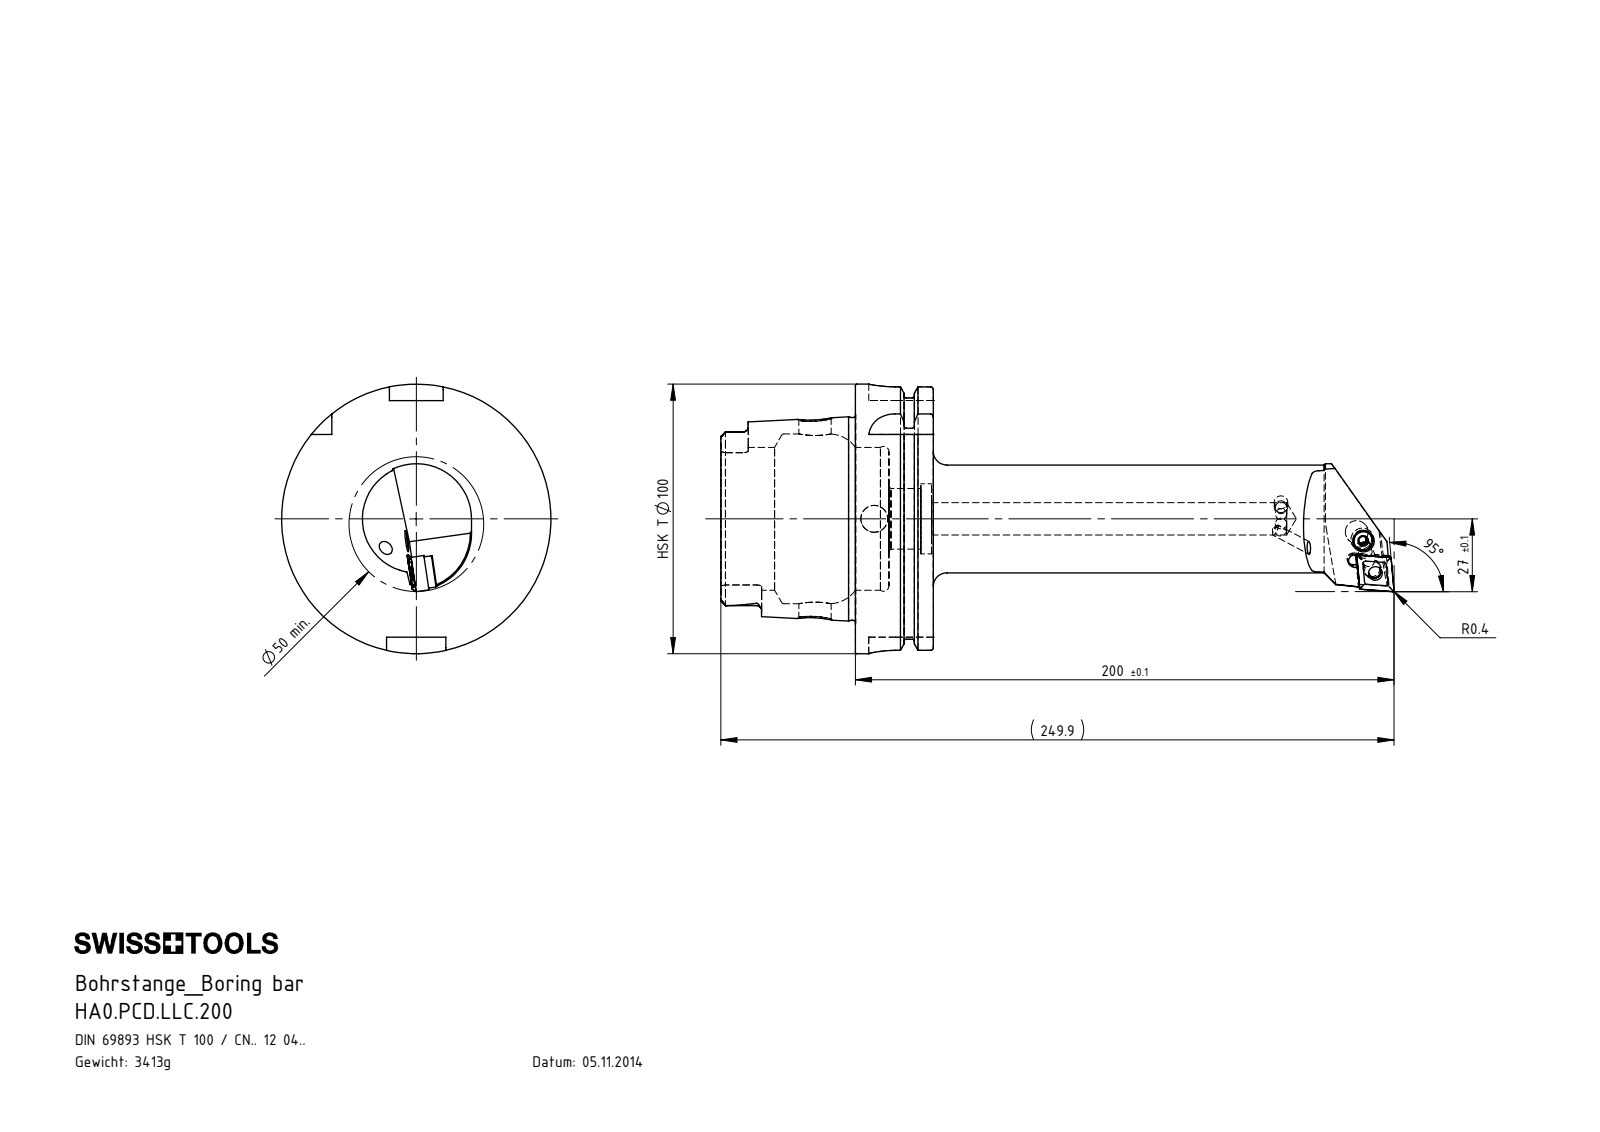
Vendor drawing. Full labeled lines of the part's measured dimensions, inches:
Part name (STEP PRODUCT): WCD-ER3.101.000_A; WCD-ER4.101.017_A; KVT_MB_600_050; CNMG120404 (+3 more)
STEP written by: SolidWorks 2017 (AUTOMOTIVE_DESIGN)
Units: inches
Bodies: 7 solids, 281 faces (112 planar, 69 cylindrical, 100 other)
Overall size (bounding box): 9.839 × 3.937 × 3.937
Volume: 26.47 in³ · Surface area: 120.8 in²
Round holes (diameter × count): ⌀0.165 ×2, ⌀0.472 ×2, ⌀0.157 ×1, ⌀0.203 ×1, ⌀0.252 ×1, ⌀0.276 ×1, ⌀0.331 ×1, ⌀0.394 ×1, ⌀0.886 ×1, ⌀1.024 ×1, ⌀2.087 ×1, ⌀2.48 ×1
Round bosses / shafts (diameter × count): ⌀3.937 ×1, ⌀3.62 ×1, ⌀2.963 ×1, ⌀1.575 ×1, ⌀0.315 ×1, ⌀0.311 ×1, ⌀0.252 ×1, ⌀0.197 ×1
Partial cylindrical surfaces — rounded edges, fillets, slot ends (radius × count): R0.075 ×6, R0.016 ×4, R0.039 ×4, R0.394 ×4, R0.098 ×2, R0.19 ×2, R0.192 ×2, R0.807 ×2
Main face-to-face distances: 1.14, 0.49, 0.65, 1.965, 2.455, 3.104, 3.457, 3.079, 1.114, 0.624
Hole centre spacings: 0.505, 0.507
